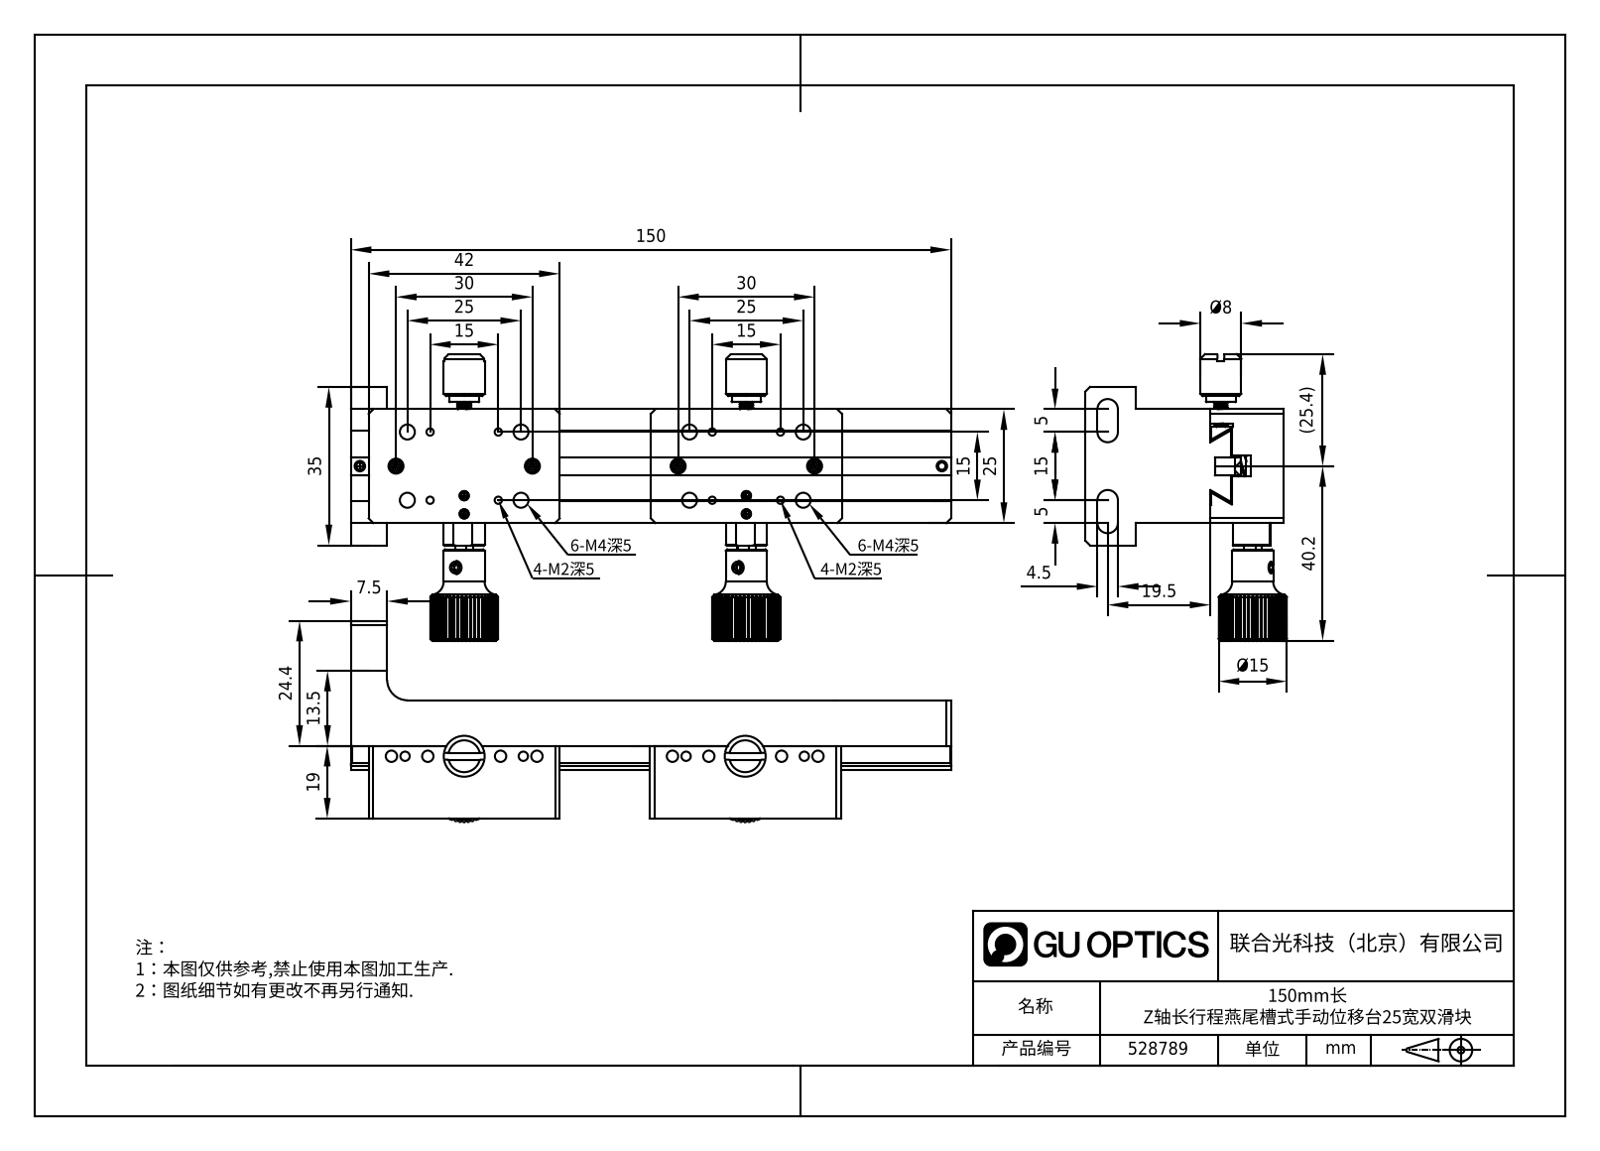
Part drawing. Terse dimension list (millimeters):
name: 528789
written by: SolidWorks 2020 (CONFIG_CONTROL_DESIGN)
unit: mm
bodies: 18 solids, 1708 faces (1029 planar, 230 cylindrical, 449 other)
size: 150 × 63.53 × 43.91
volume: 82 139 mm³; area: 38 495 mm²
holes: 13× ⌀1.6, 12× ⌀2.5, 12× ⌀3.3, 8× ⌀2.05, 3× ⌀2.4, 3× ⌀4.3, 2× ⌀2.3, 2× ⌀4, 2× ⌀4.5, 2× ⌀8
bosses: 4× ⌀9, 4× ⌀2.5, 2× ⌀7, 2× ⌀6.85, 2× ⌀6.5, 2× ⌀3.8, 2× ⌀2.95, 2× ⌀2
rounds: 12× R0.2, 8× R2.25, 3× R4.5, 2× R7.5
face distances: 14.5, 4.5, 25, 10, 11.1, 0.51, 14.7, 11.3, 10.55, 14.45
hole spacings: 50.7, 5, 15, 25, 7.91, 8, 10.61, 15.81
